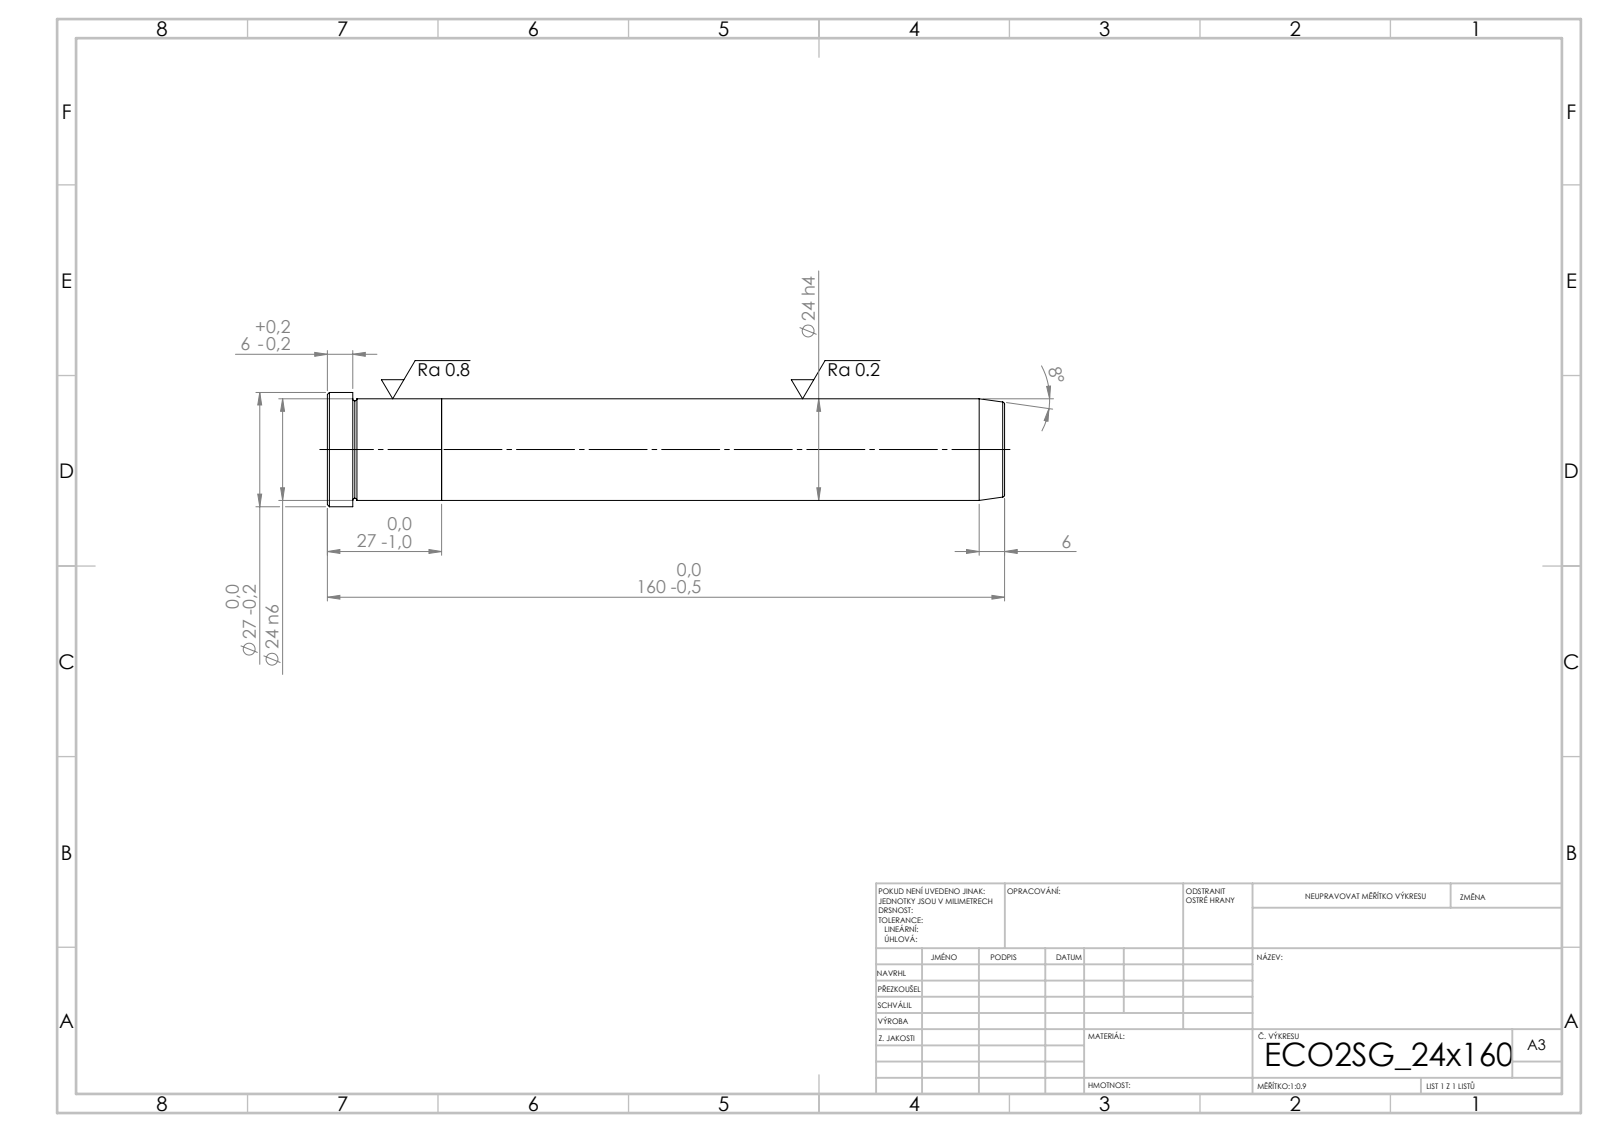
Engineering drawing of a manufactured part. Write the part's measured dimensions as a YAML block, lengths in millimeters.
step_written_by: "SolidWorks 2019 (CONFIG_CONTROL_DESIGN)"
units: millimeters
bodies: {solids: 2, faces: 21, planar: 5, cylindrical: 6, other: 10}
overall_size: [160, 27, 27]
volume: 72875
surface_area: 14101
round_bosses_or_shafts:
  - {diameter: 27, count: 1}
  - {diameter: 24, count: 1}
face_to_face_distances: [27, 133, 160, 154, 21, 6]
